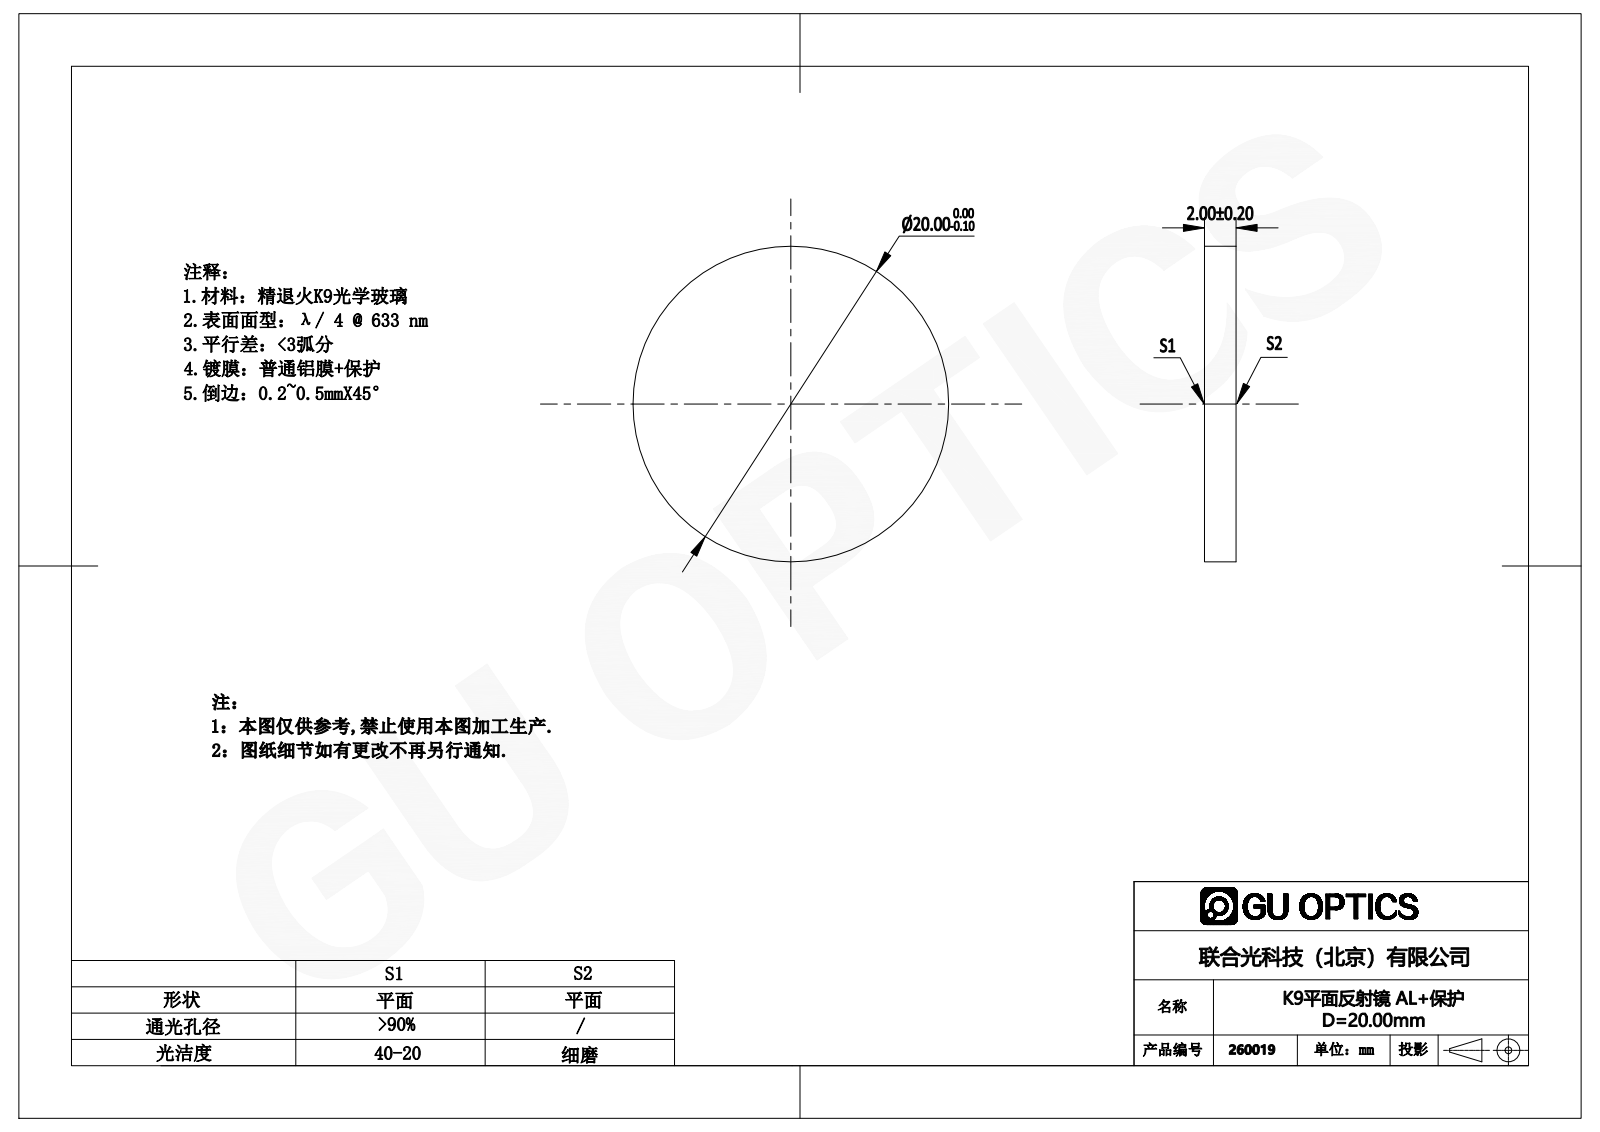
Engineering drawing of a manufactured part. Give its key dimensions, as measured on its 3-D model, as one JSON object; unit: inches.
{"part_name": "260006", "step_written_by": "SolidWorks 2016 (AUTOMOTIVE_DESIGN)", "units": "inches", "bodies": {"solids": 1, "faces": 4, "planar": 2, "cylindrical": 2, "other": 0}, "overall_size": [0.787, 0.787, 0.079], "volume_in3": 0.038, "surface_area_in2": 1.17, "round_bosses_or_shafts": [[0.787, 1]], "face_to_face_distances": [0.079]}
